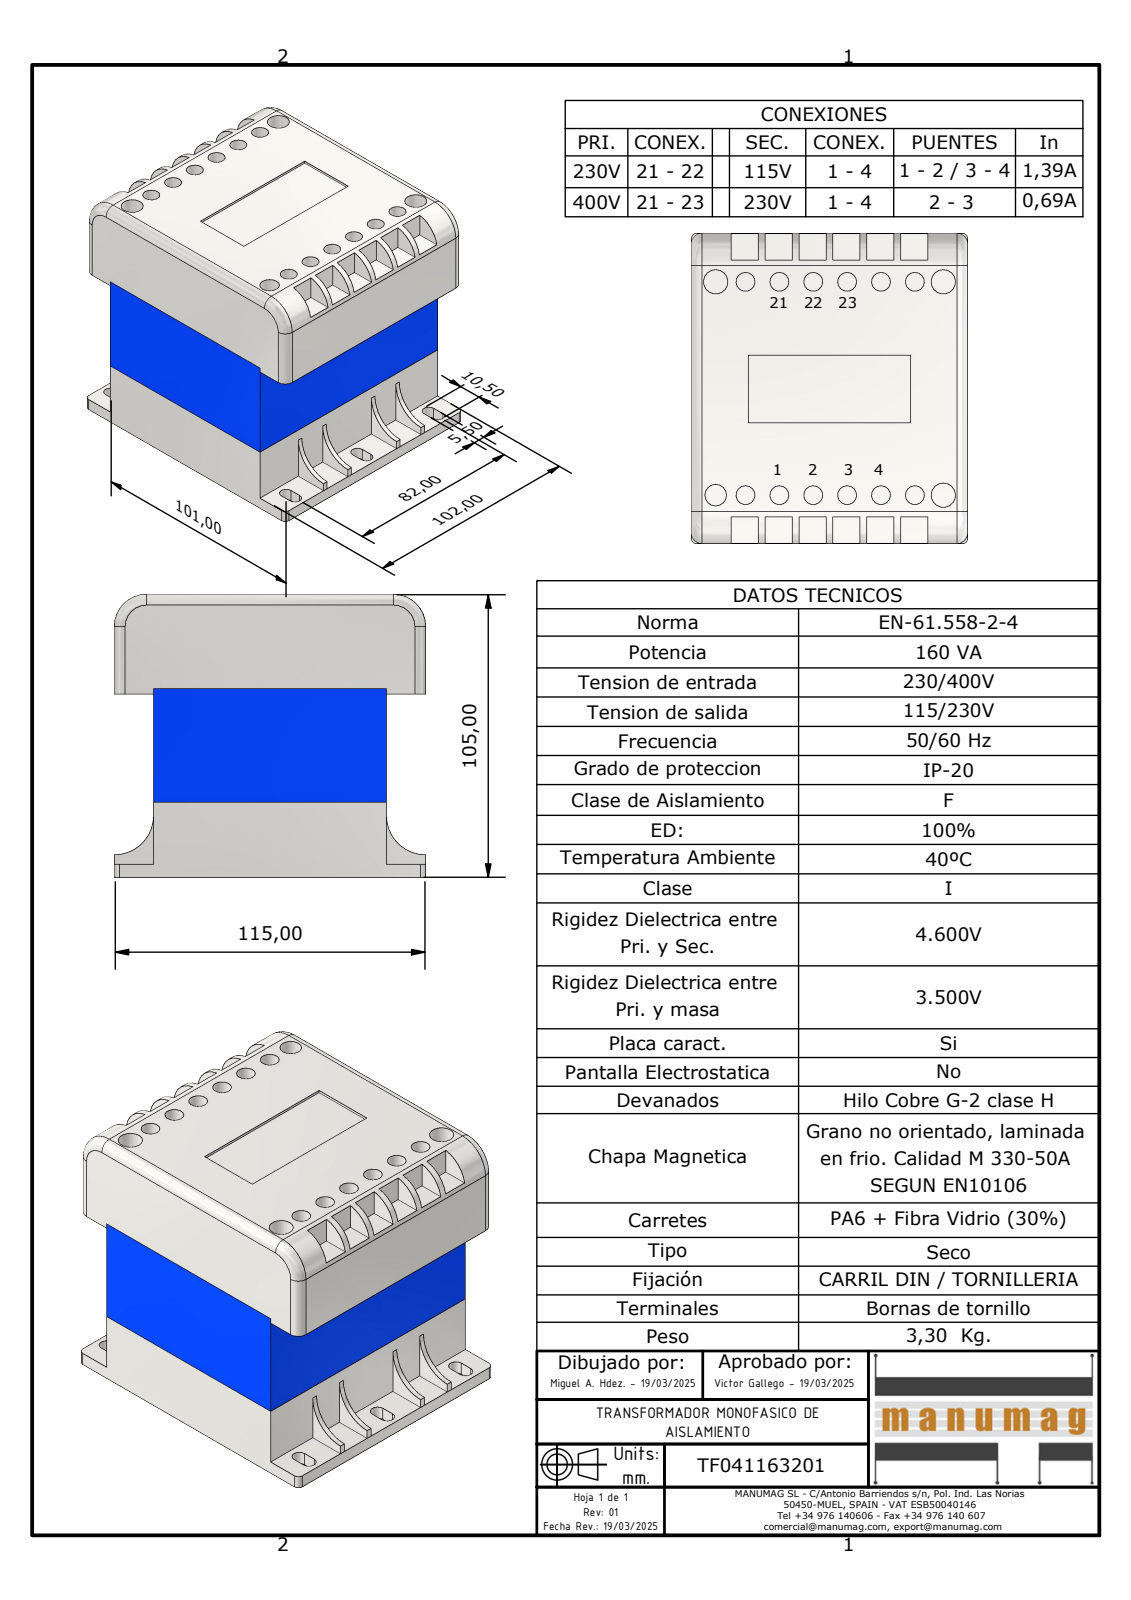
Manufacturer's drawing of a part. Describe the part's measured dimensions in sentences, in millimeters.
The part is named "TF041163201; INFERIOR EI96; CENTRAL EI96-40; SUPERIOR EI96". Its 3-D file was written by "Autodesk Inventor 2023 (AUTOMOTIVE_DESIGN)". It is 11 solids with 200 faces: 152 planar, 44 cylindrical and 4 other. Overall it measures 115 by 105 by 102 millimeters. Its volume is 475 560 cubic millimeters and its surface area 121 267 square millimeters. Round holes: 12 of diameter 7, 3 of diameter 9, 1 of diameter 8. Partial cylindrical surfaces (rounded edges, fillets, slot ends): 8 of radius 2.5, 6 of radius 4, 4 of radius 2, 2 of radius 12, 2 of radius 14.5. The main face-to-face distances are 1, 85, 100, 5, 101, 65, 102, 70, 105, 35. The hole center spacings are 12.5, 79.98, 25, 79, 82.86, 37.5, 87.45, 50.
